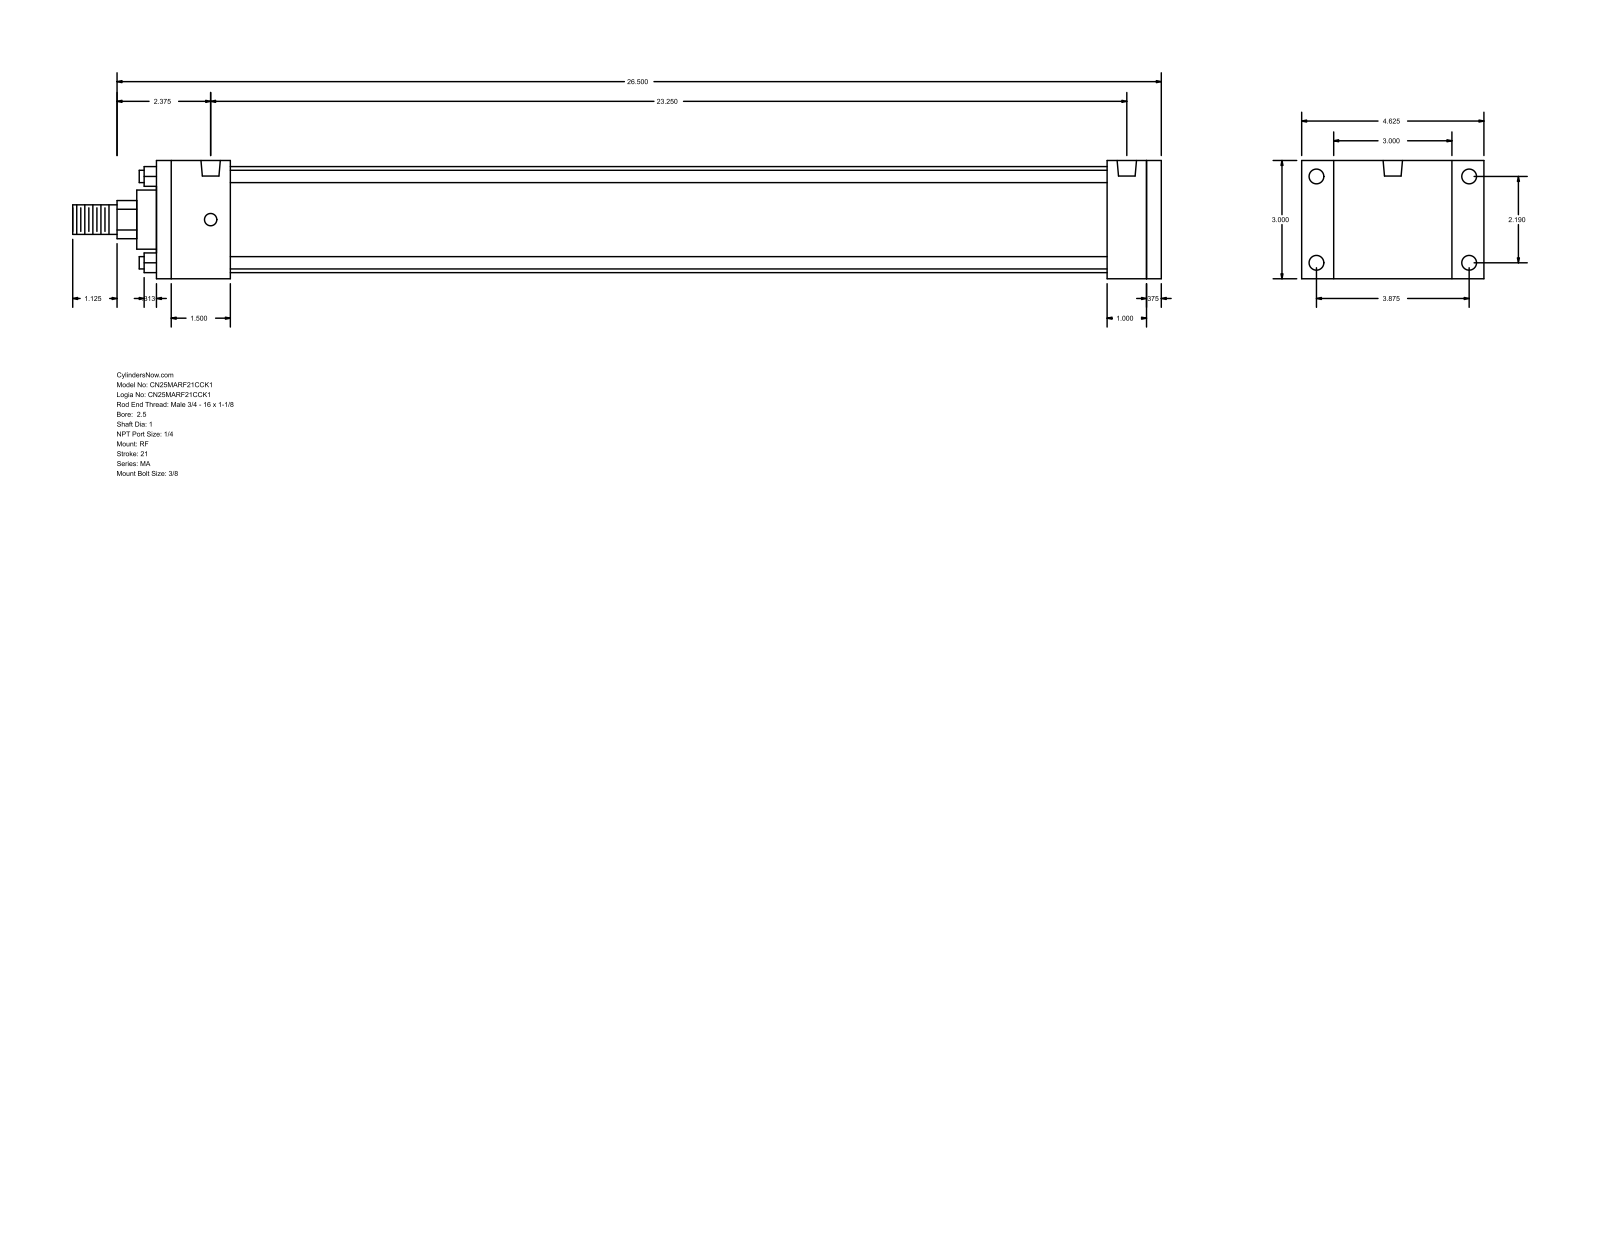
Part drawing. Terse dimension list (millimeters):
name: MA_RF__0250_1
written by: GSSL Pune (CONFIG_CONTROL_DESIGN)
unit: mm
bodies: 0 solids, 92 faces (64 planar, 28 cylindrical, 0 other)
size: 701.67 × 117.47 × 76.2
holes: 4× ⌀7.94, 4× ⌀9.53, 2× ⌀12.49
bosses: 4× ⌀7.94, 1× ⌀68.33, 1× ⌀38.1, 1× ⌀25.4, 1× ⌀19.05
rounds: 1× R12.29
face distances: 76.2, 647.7, 638.18, 9.52, 47.63, 612.77, 565.14, 590.55, 600.07, 25.41
hole spacings: 55.62, 98.42, 113.05, 590.55
